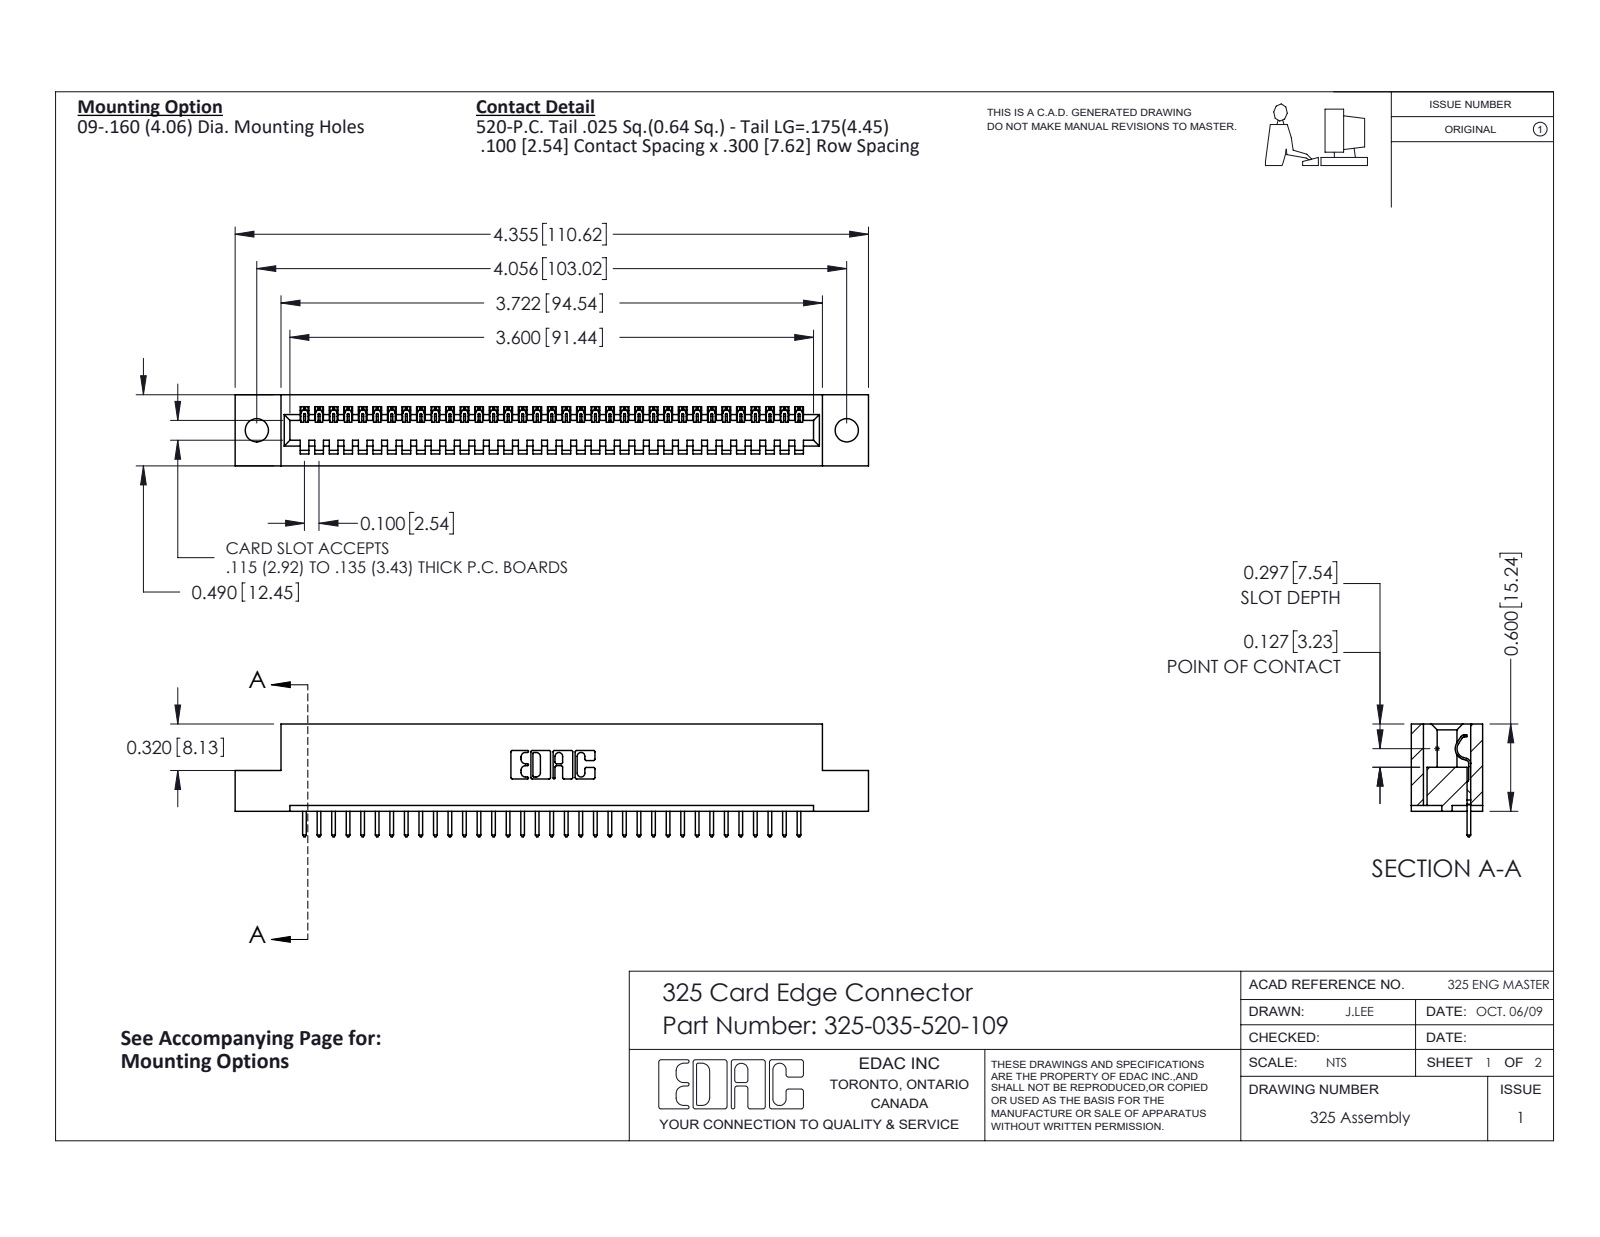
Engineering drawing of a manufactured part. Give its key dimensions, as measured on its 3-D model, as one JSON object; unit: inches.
{"part_name": "325-035-520-109; 325 Part_.160 TH; 325-292-001_325-293-120", "step_written_by": "SolidWorks 2016 (CONFIG_CONTROL_DESIGN)", "units": "inches", "bodies": {"solids": 36, "faces": 2144, "planar": 1540, "cylindrical": 604, "other": 0}, "overall_size": [4.355, 0.775, 0.49], "volume_in3": 0.834, "surface_area_in2": 22.23, "round_holes": [[0.16, 2]], "partial_cylinders_radius": [[0.006, 70], [0.01, 70], [0.01, 22], [0.007, 6], [0.031, 6], [0.026, 3], [0.014, 1], [0.022, 1]], "face_to_face_distances": [0.083, 0.407, 0.49, 0.3, 0.107, 0.383, 0.025, 0.325, 0.56, 0.04], "hole_center_spacings": [4.056]}
